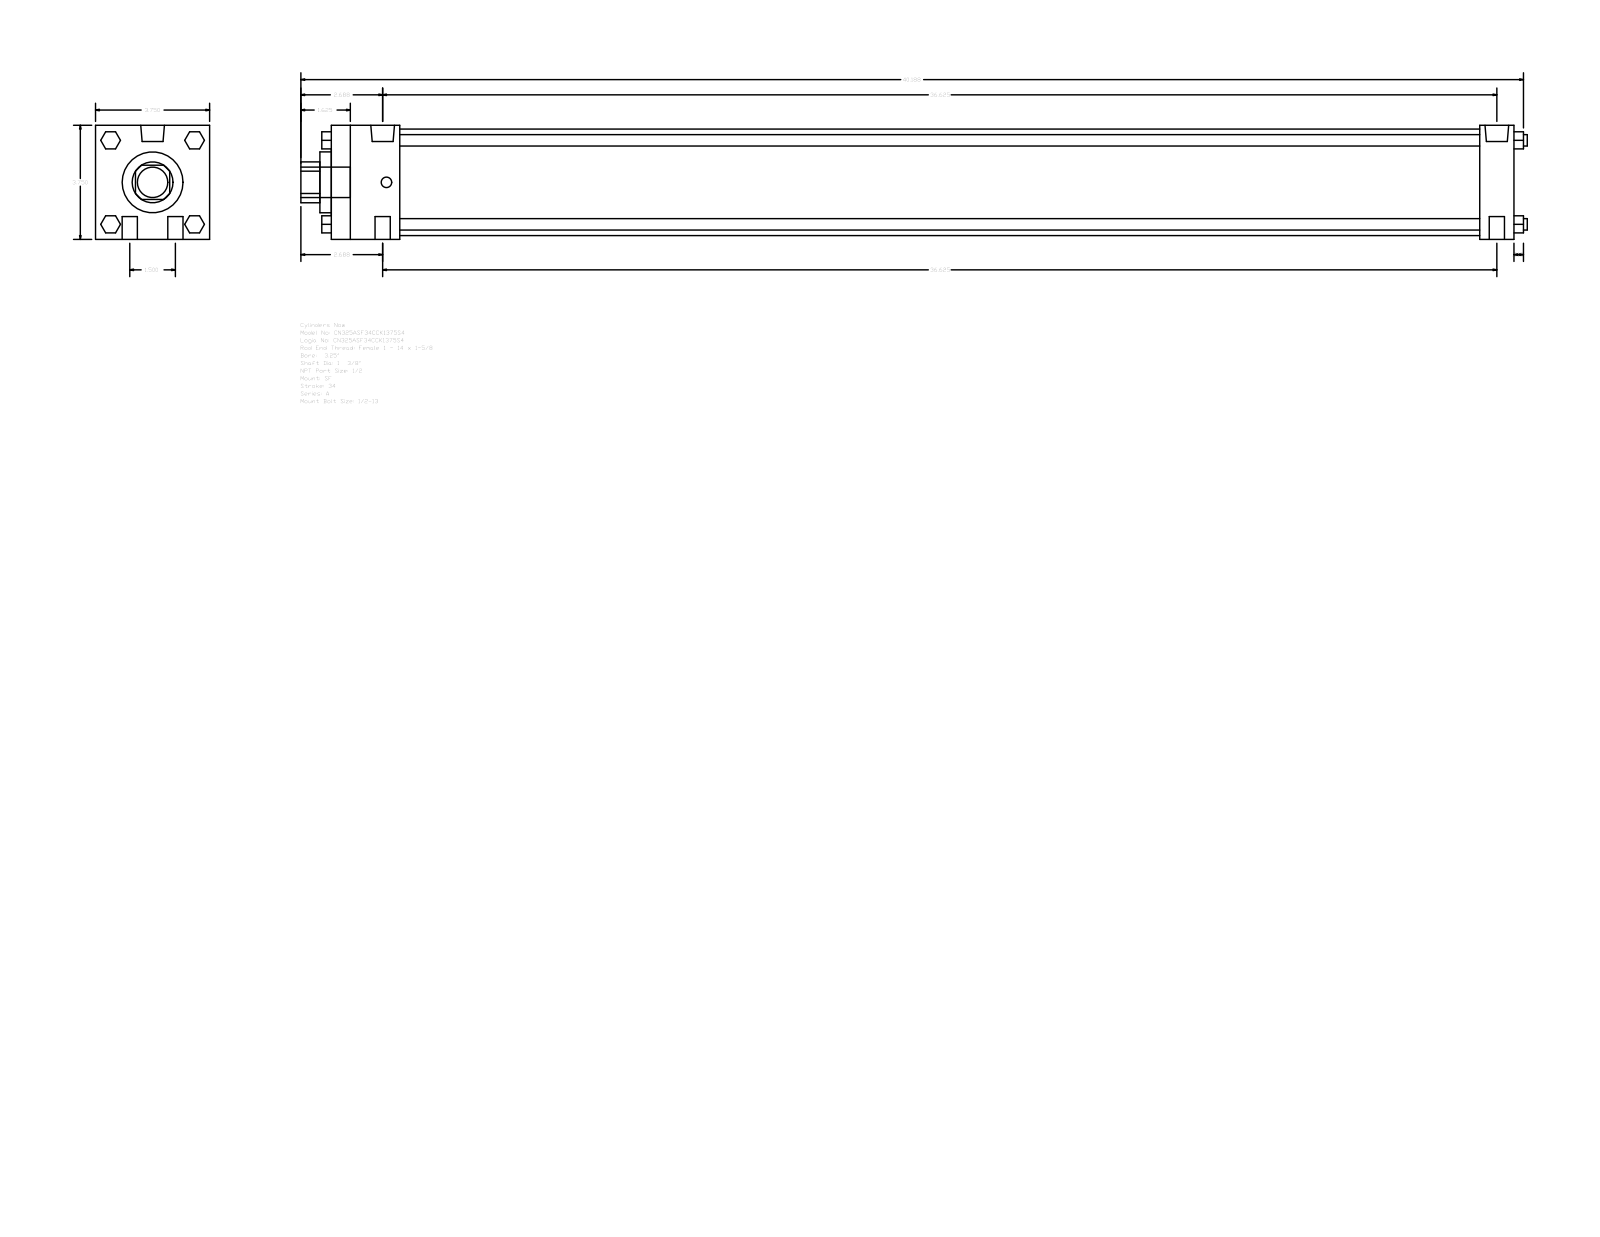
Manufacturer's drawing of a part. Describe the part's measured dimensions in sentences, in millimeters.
The part is named "A_SF__0325_1.375". Its 3-D file was written by "GSSL Pune (CONFIG_CONTROL_DESIGN)". It is 0 solids with 124 faces: 94 planar, 30 cylindrical and 0 other. Overall it measures 1023.94 by 95.25 by 95.25 millimeters. Round holes: 1 of diameter 34.92, 1 of diameter 50.8, 1 of diameter 88.9. Round bosses or shafts: 4 of diameter 12.7, 4 of diameter 9.53, 2 of diameter 19.77, 2 of diameter 8.73, 1 of diameter 25.4. Partial cylindrical surfaces (rounded edges, fillets, slot ends): 1 of radius 17.06. The main face-to-face distances are 95.24, 987.43, 28.58, 958.85, 57.15, 901.7, 930.28, 9.52, 66.67, 968.37.
